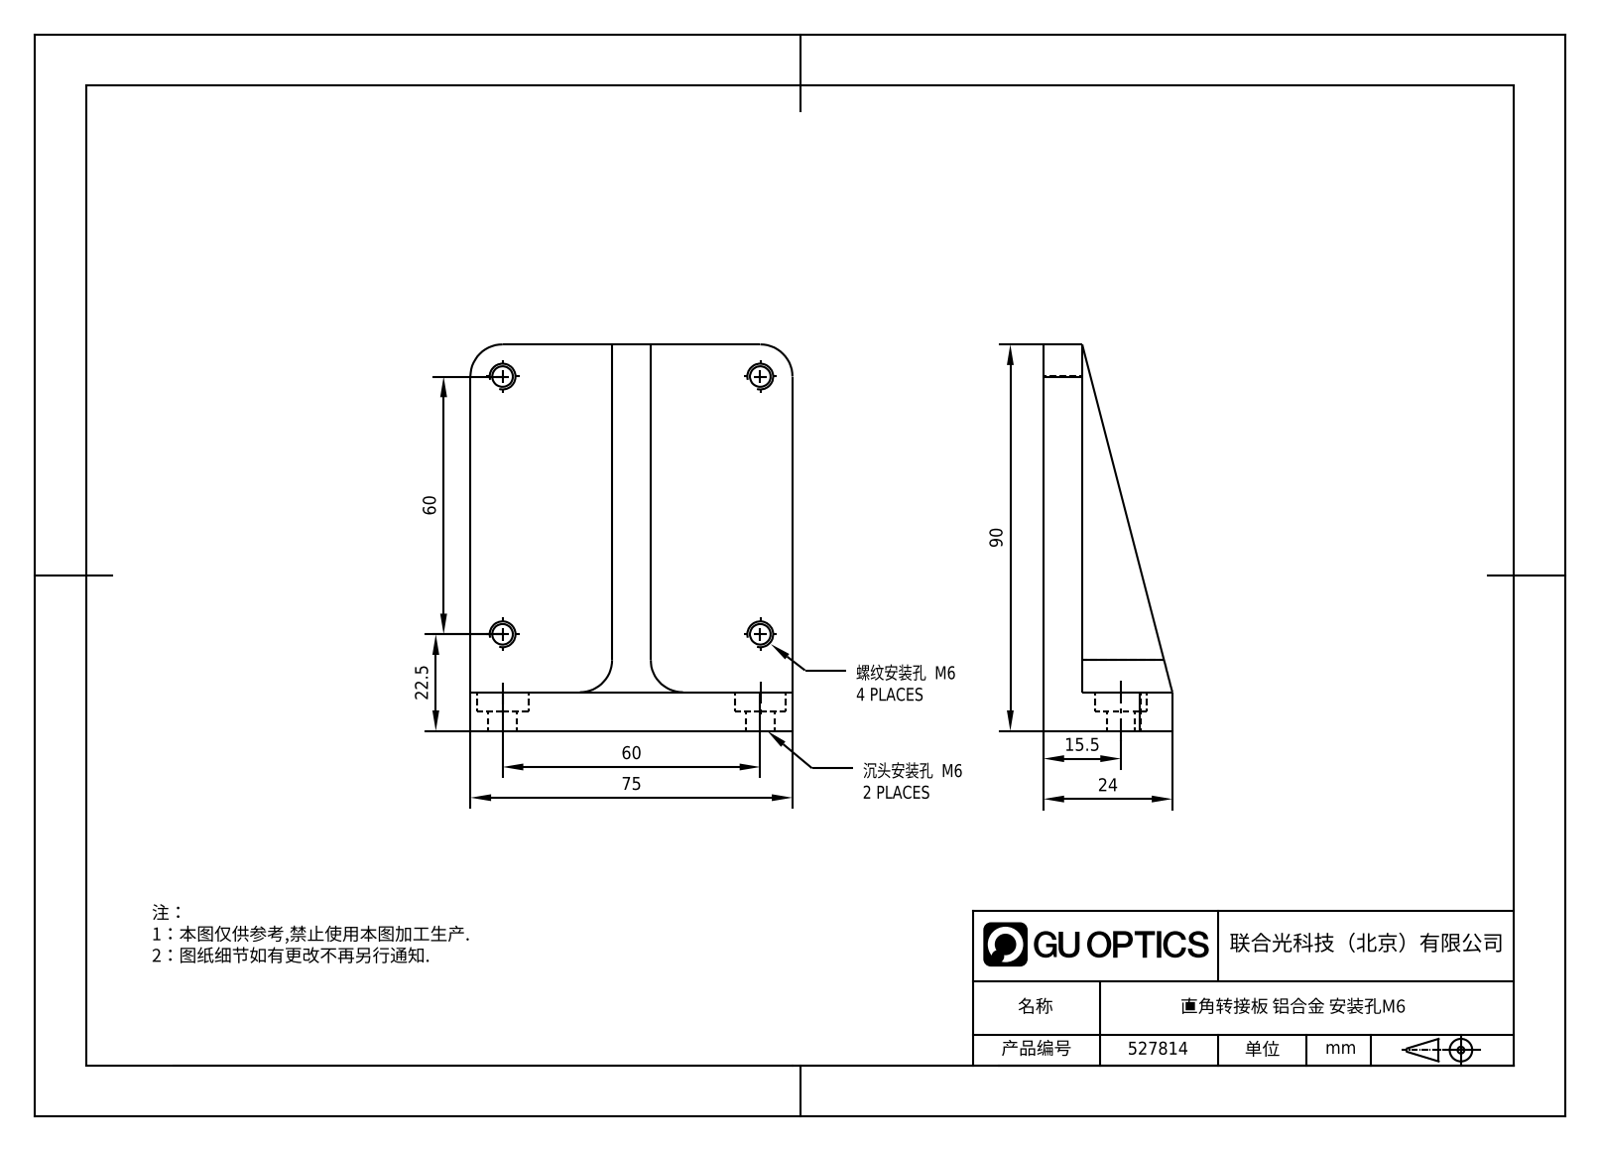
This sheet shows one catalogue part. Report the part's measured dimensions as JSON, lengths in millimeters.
{"part_name": "1.6.9.6_ZSJ-Z075_75mm直角转接板，带M6螺孔和M6沉头孔", "step_written_by": "SolidWorks 2021 (CONFIG_CONTROL_DESIGN)", "units": "millimeters", "bodies": {"solids": 1, "faces": 37, "planar": 15, "cylindrical": 22, "other": 0}, "overall_size": [90, 75, 24], "volume_mm3": 67062, "surface_area_mm2": 20370, "round_holes": [[5, 4], [6.5, 2], [11, 2]], "partial_cylinders_radius": [[7.5, 6]], "face_to_face_distances": [8, 33.5, 41.5, 75, 90, 82, 24, 16, 3, 5], "hole_center_spacings": [60, 84.85]}
